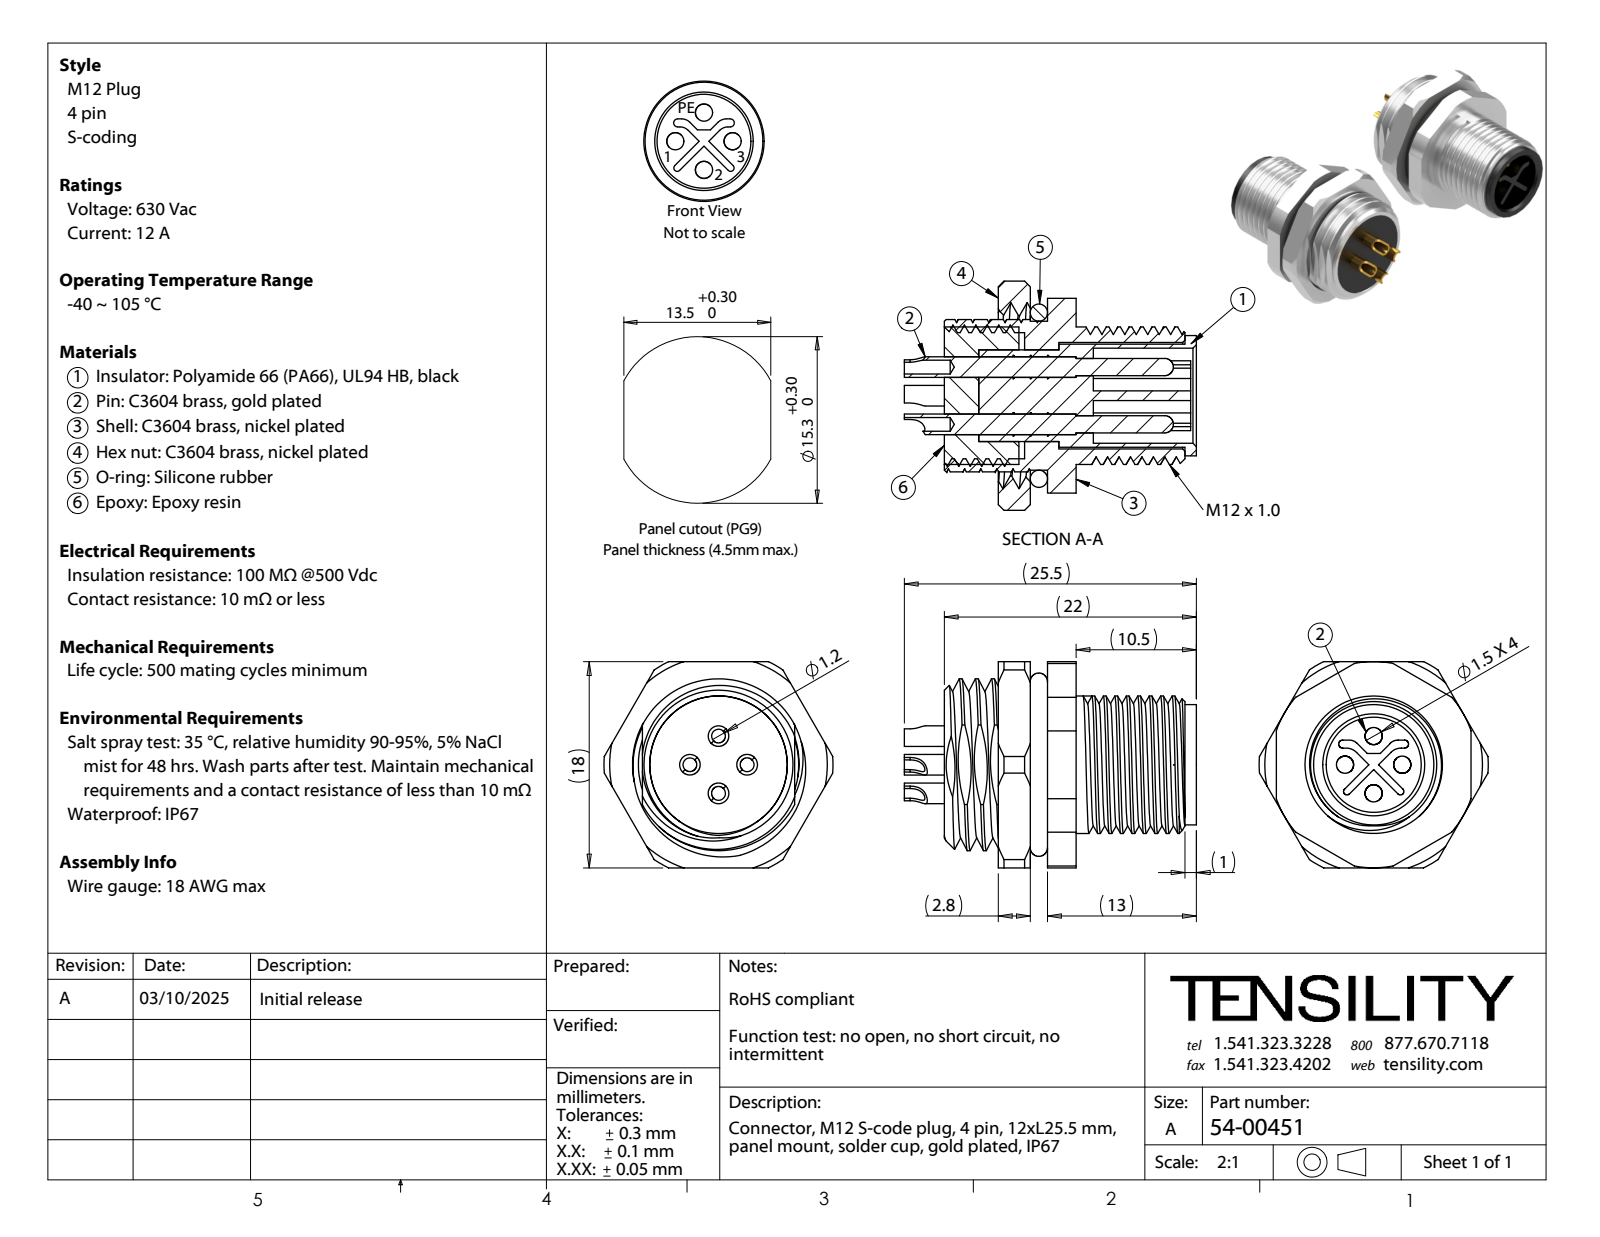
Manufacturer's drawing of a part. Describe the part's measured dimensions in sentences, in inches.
The part is named "54-00451-03; 54-00451-04; 54-00451-05; 54-00451_revA (+3 more)". Its 3-D file was written by "SolidWorks 2021 (CONFIG_CONTROL_DESIGN)". It is 9 solids with 348 faces: 91 planar, 163 cylindrical and 94 other. Overall it measures 1.004 by 0.787 by 0.709 inches. Its volume is 0.184 cubic inches and its surface area 9.171 square inches. Round holes: 4 of diameter 0.047, 4 of diameter 0.059, 1 of diameter 0.315, 1 of diameter 0.327, 1 of diameter 0.366, 1 of diameter 0.433, 1 of diameter 0.551. Round bosses or shafts: 4 of diameter 0.071, 1 of diameter 0.512, 1 of diameter 0.472, 1 of diameter 0.413, 1 of diameter 0.354. Partial cylindrical surfaces (rounded edges, fillets, slot ends): 2 of radius 0.012, 2 of radius 0.014, 2 of radius 0.039, 2 of radius 0.05, 2 of radius 0.067, 1 of radius 0.295, 1 of radius 0.354, 1 of radius 0.394. The main face-to-face distances are 0.098, 0.157, 0.059, 0.118, 0.453, 0.354, 0.177, 0.236, 0.039, 0.709. The hole center spacings are 0.098, 0.139, 0.197.
